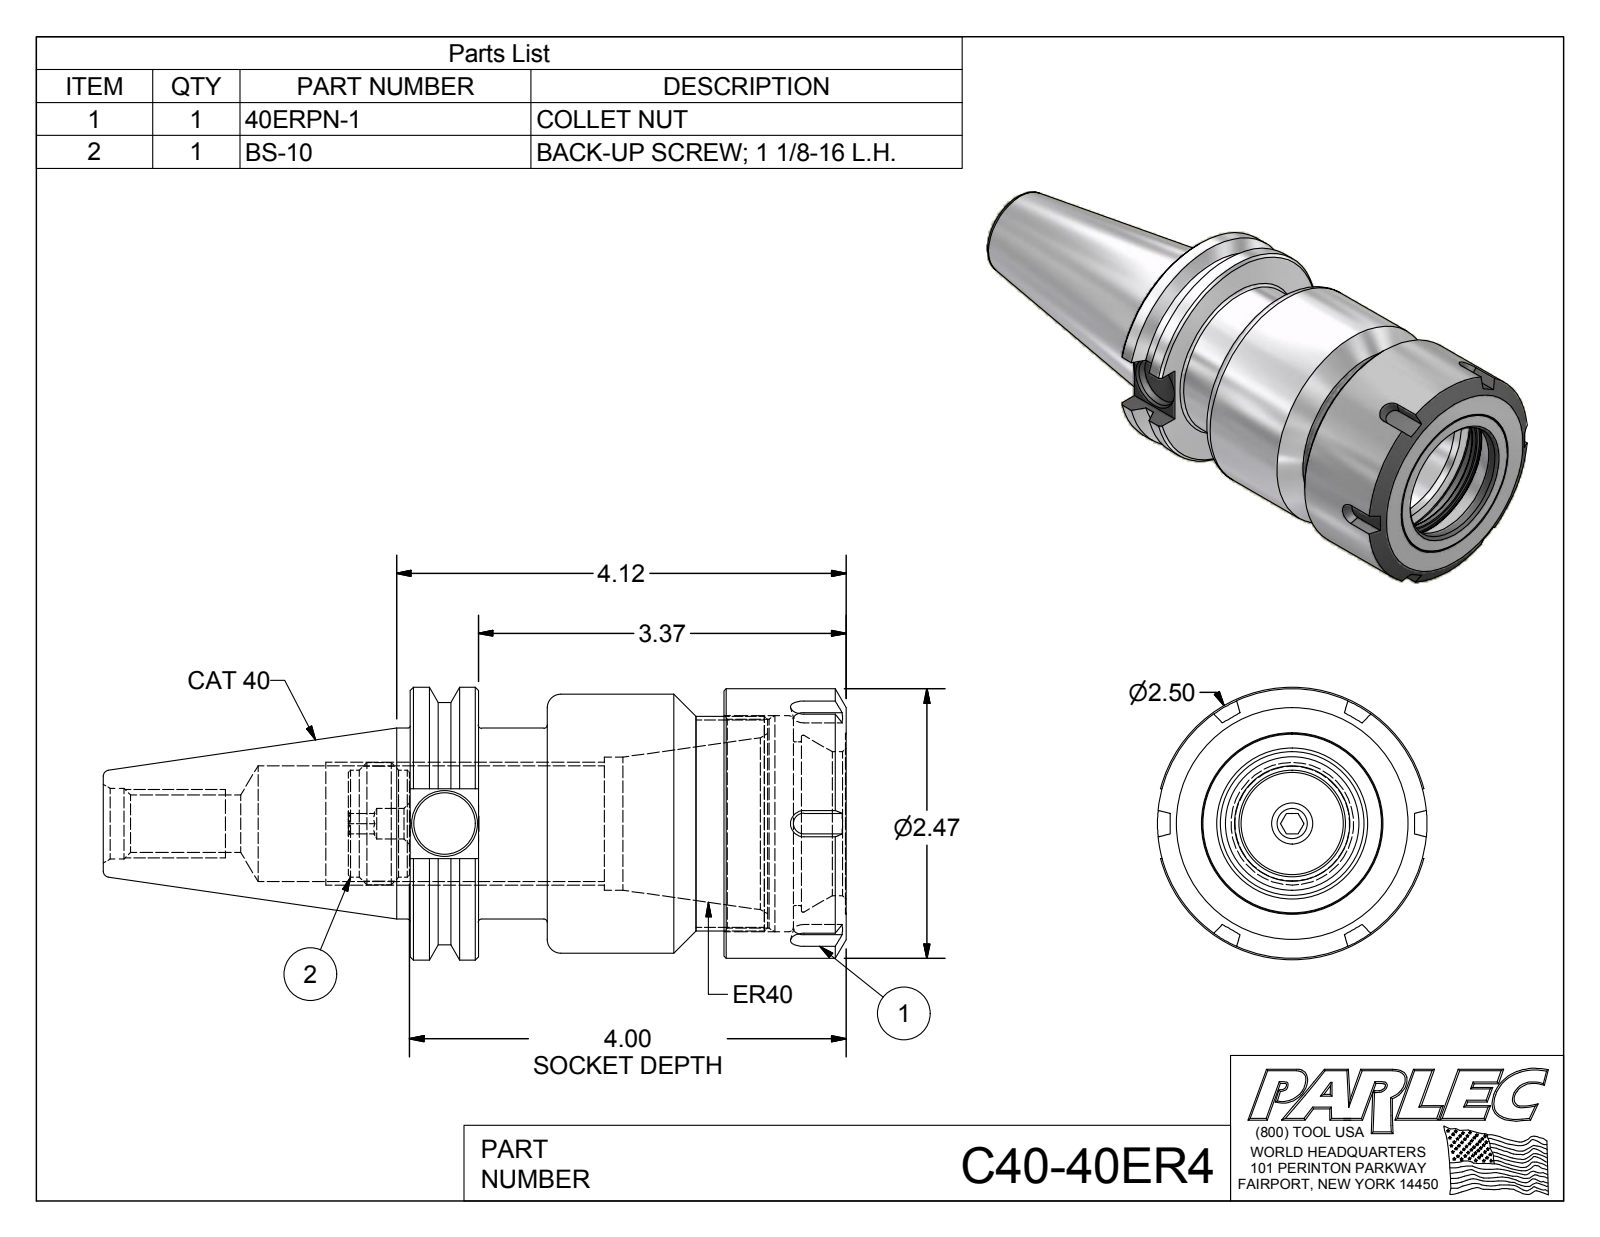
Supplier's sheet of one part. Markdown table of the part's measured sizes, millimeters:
| quantity | value |
| --- | --- |
| part name | C40-40ER4; C40-40ER4-1; 40ERPN; BS-10 |
| STEP written by | Autodesk Inventor 2012 (AUTOMOTIVE_DESIGN) |
| units | millimeters |
| bodies | 3 solids, 118 faces (43 planar, 26 cylindrical, 49 other) |
| overall size | 172.9 × 63.5 × 62.7 |
| volume | 227 600 mm³ |
| surface area | 57 450 mm² |
| round holes (diameter × count) | 5.6 × 1, 7.1 × 1, 13.4 × 1, 14.3 × 1, 16.5 × 1, 26.8 × 1, 31 × 1, 33.5 × 1, 38.1 × 1, 41.1 × 1, 48.7 × 1, 50.3 × 1 |
| round bosses / shafts (diameter × count) | 63.5 × 1, 62.7 × 1, 60.3 × 1, 56.4 × 1, 50 × 1, 44.5 × 1, 28.4 × 1, 24.9 × 1 |
| main face-to-face distances | 101.5, 15.9, 85.6, 73, 57.2, 28.4, 89.2, 73.3, 16.2, 12.3 |
